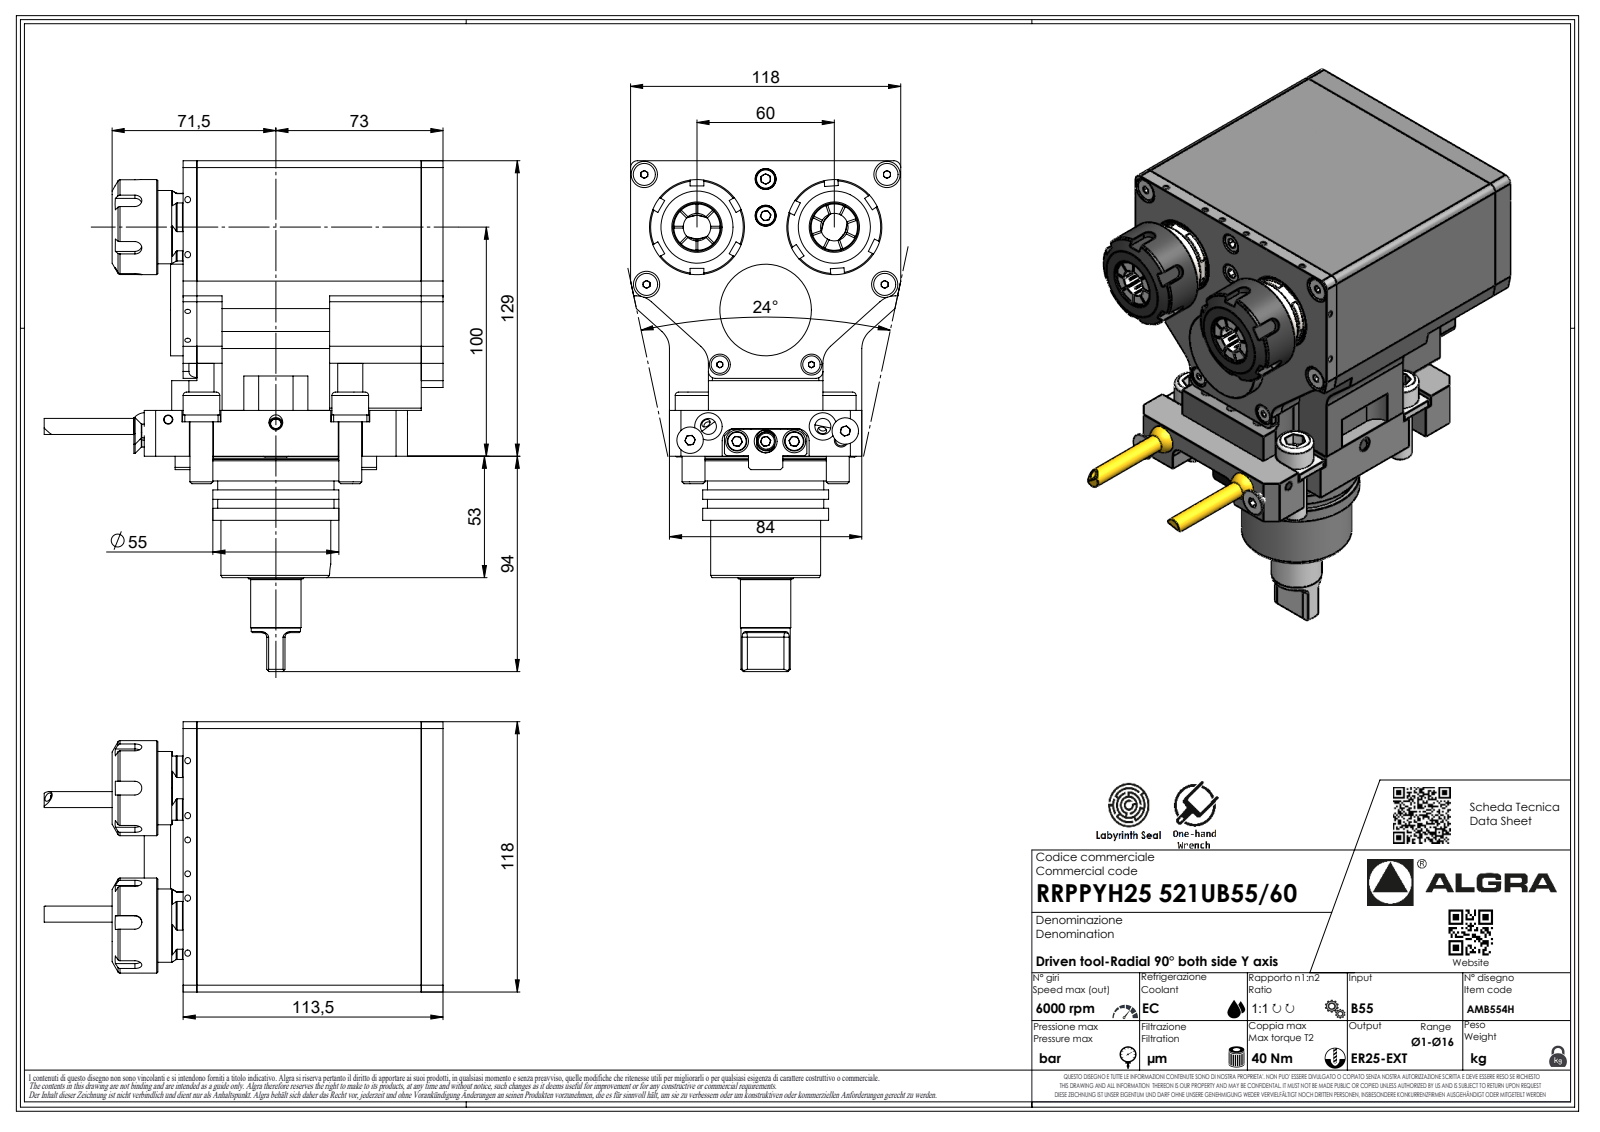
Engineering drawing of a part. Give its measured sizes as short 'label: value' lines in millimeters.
name: RRPPYH25521UB5560
written by: SolidWorks 2023 (AUTOMOTIVE_DESIGN)
unit: mm
bodies: 1 solid, 794 faces (471 planar, 153 cylindrical, 170 other)
size: 223 × 174.2 × 118
volume: 1 576 000 mm³; area: 121 970 mm²
holes: 2× ⌀4, 1× ⌀2.1, 1× ⌀43.5
bosses: 4× ⌀16, 4× ⌀10, 2× ⌀41.5, 2× ⌀32, 2× ⌀7, 1× ⌀55, 1× ⌀54.6, 1× ⌀50.8
rounds: 17× R3, 10× R1, 10× R10, 8× R2, 7× R0.33, 7× R0.52, 7× R3.7, 6× R5.25
face distances: 17, 113.5, 118, 101, 129, 84, 34, 20, 109, 8
